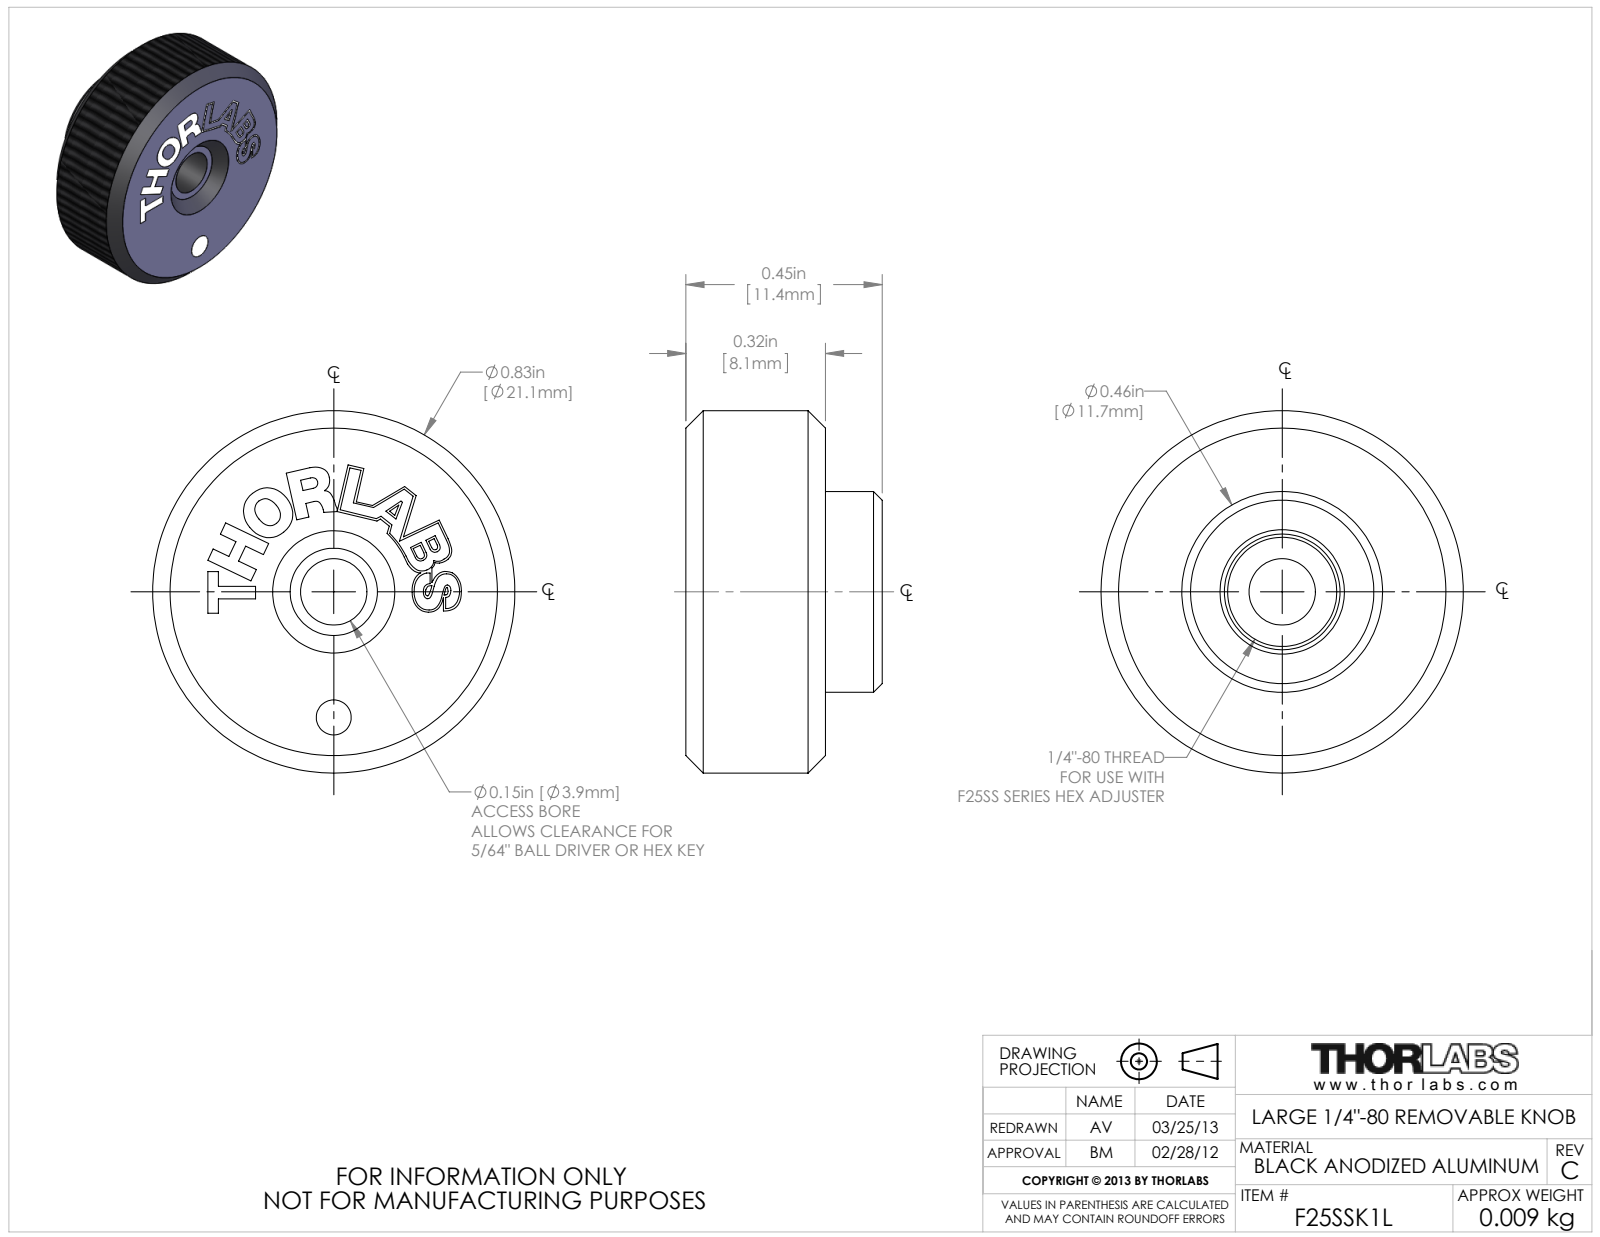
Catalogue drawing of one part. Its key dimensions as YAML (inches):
part_name: "23766-E0W"
step_written_by: "SolidWorks 2012 (AUTOMOTIVE_DESIGN)"
units: inches
bodies: {solids: 1, faces: 194, planar: 107, cylindrical: 16, other: 71}
overall_size: [0.83, 0.83, 0.45]
volume: 0.175
surface_area: 2.221
round_holes:
  - {diameter: 0.08, count: 1}
  - {diameter: 0.152, count: 1}
  - {diameter: 0.25, count: 1}
  - {diameter: 0.265, count: 1}
  - {diameter: 0.29, count: 1}
round_bosses_or_shafts:
  - {diameter: 0.83, count: 1}
  - {diameter: 0.46, count: 1}
partial_cylinders:
  - {radius: 0.184, count: 2}
face_to_face_distances: [0.32, 0.45, 0.13, 0.27, 0.05, 0.18, 0.03, 0.3, 0.02, 0.15]
hole_center_spacings: [0.287]
